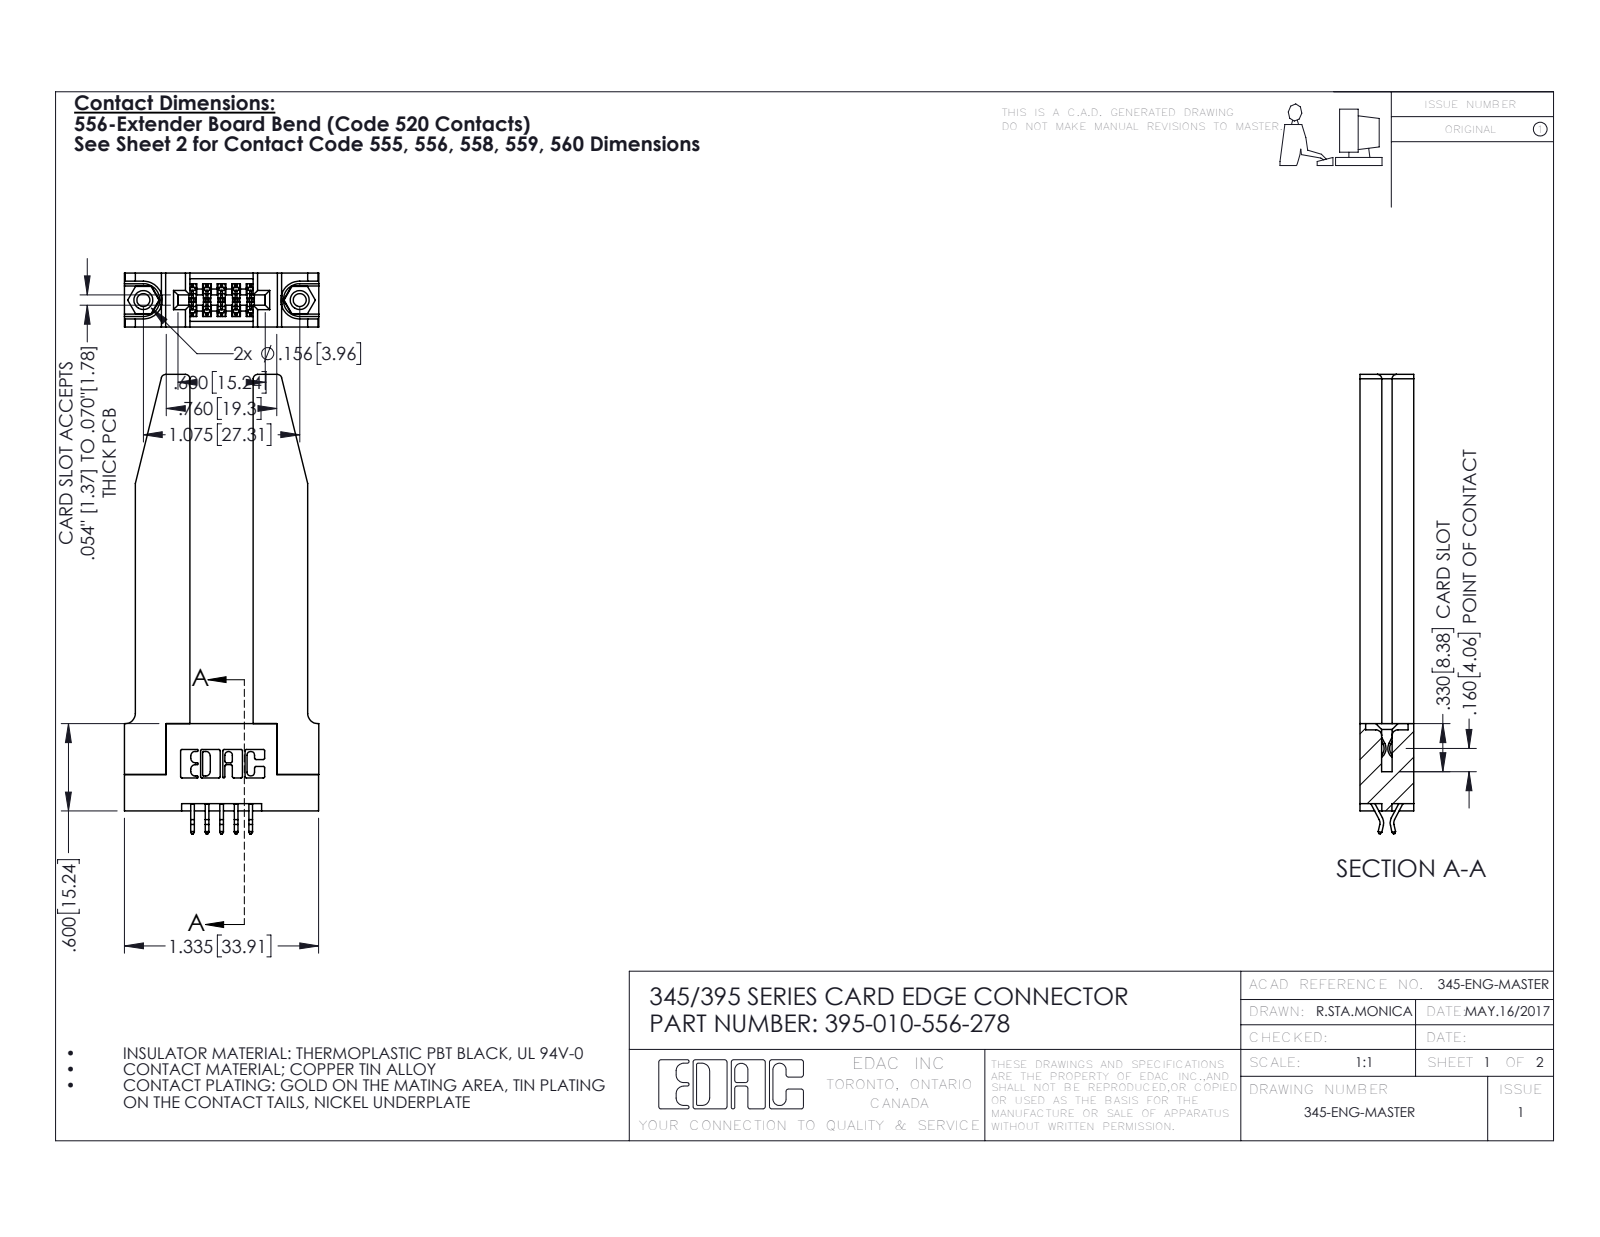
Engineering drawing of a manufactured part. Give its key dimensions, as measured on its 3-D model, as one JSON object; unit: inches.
{"part_name": "345-220-078_345-220-078; 345 Part_Flush Mounting Lugs - 0.156 Dia-TH; 395-010-556-278; 345-292-001_556 Tail (+1 more)", "step_written_by": "SolidWorks 2016 (CONFIG_CONTROL_DESIGN)", "units": "inches", "bodies": {"solids": 15, "faces": 920, "planar": 592, "cylindrical": 276, "other": 52}, "overall_size": [3.157, 1.336, 0.37], "volume_in3": 0.654, "surface_area_in2": 16.24, "round_holes": [[0.089, 2], [0.125, 2], [0.156, 2], [0.064, 1]], "round_bosses_or_shafts": [[0.155, 2]], "partial_cylinders_radius": [[0.01, 22], [0.006, 15], [0.03, 8], [0.007, 6], [0.031, 6], [0.026, 3], [0.01, 2], [0.014, 2]], "face_to_face_distances": [0.37, 0.15, 0.22, 0.435, 0.072, 0.148, 0.077, 0.298, 0.2, 0.095], "hole_center_spacings": [0.27, 0.847, 1.075]}
